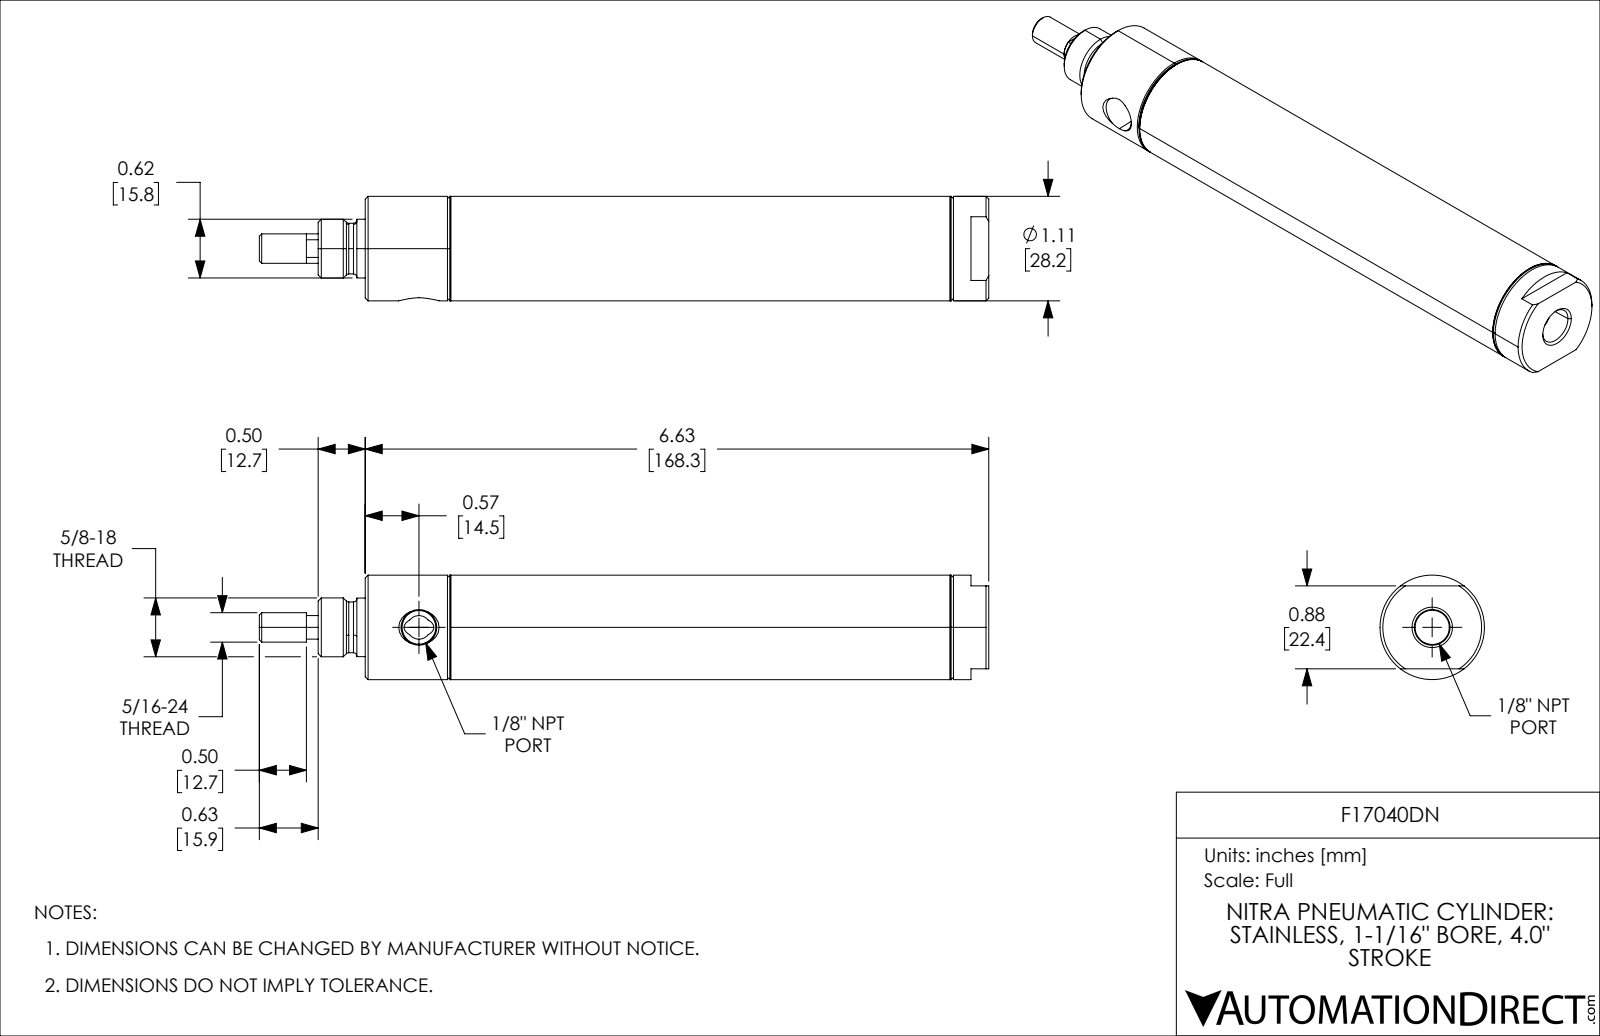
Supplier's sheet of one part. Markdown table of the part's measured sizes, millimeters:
| quantity | value |
| --- | --- |
| part name | F17040DN_1; F17040DN; F17040DN_7; F17040DN_5 (+1 more) |
| STEP written by | SolidWorks 2021 (CONFIG_CONTROL_DESIGN) |
| units | millimeters |
| bodies | 4 solids, 125 faces (25 planar, 44 cylindrical, 56 other) |
| overall size | 196.85 × 28.19 × 28.19 |
| volume | 49 961 mm³ |
| surface area | 40 005 mm² |
| round holes (diameter × count) | 8.53 × 1, 9.25 × 1, 19.05 × 1, 25.7 × 1 |
| round bosses / shafts (diameter × count) | 28.19 × 1, 27.23 × 1, 15.88 × 1, 15.81 × 1, 13.68 × 1, 7.94 × 1, 7.92 × 1 |
| partial cylindrical surfaces (radius × count) | 3.17 × 1 |
| main face-to-face distances | 22.22, 101.6, 123.82, 139.7, 38.1, 15.88, 28.58, 130.18, 152.4, 168.28 |
